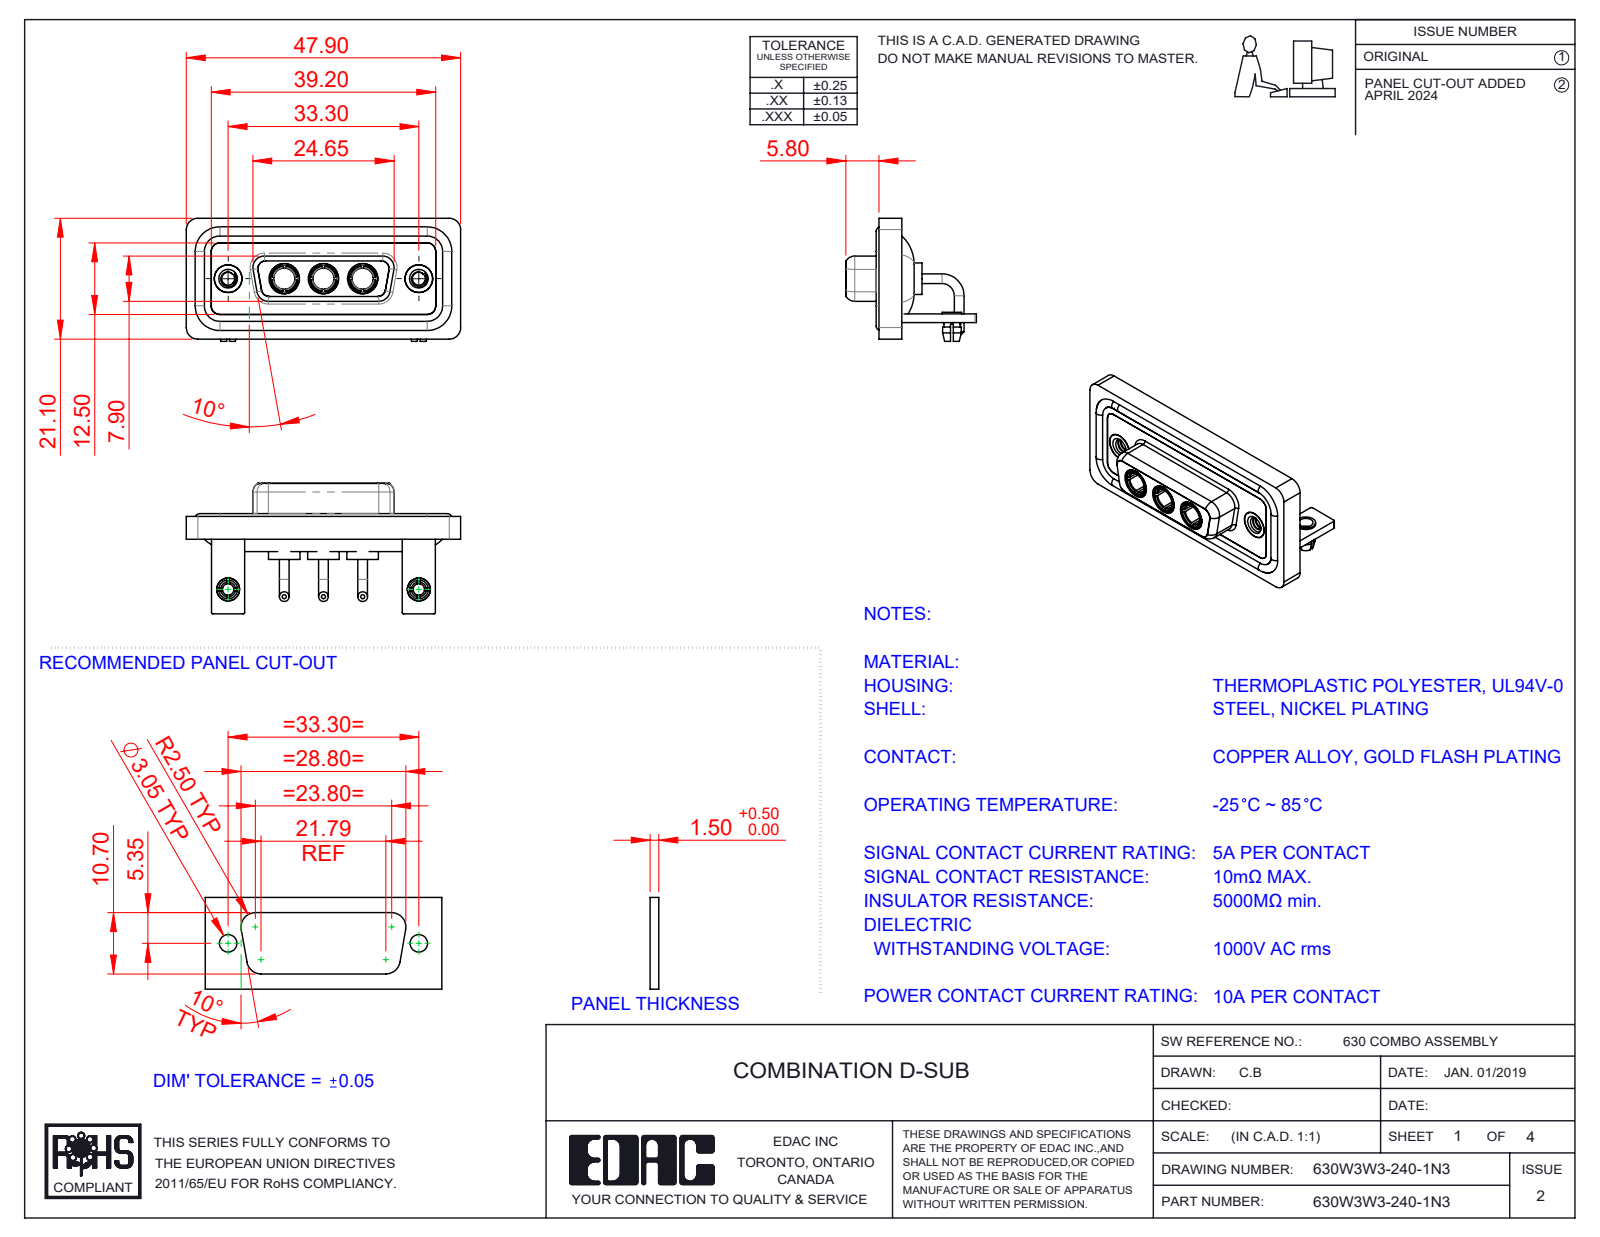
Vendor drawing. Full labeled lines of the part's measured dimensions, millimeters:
Part name (STEP PRODUCT): 630Combo Board Lock_50 Contacts; 630Combo Shell Rear_15 Contacts; 630W3W3-140-1N3; 630Combo Housing_3W3 (+5 more)
STEP written by: SolidWorks 2023 (CONFIG_CONTROL_DESIGN)
Units: millimetres
Bodies: 17 solids, 760 faces (260 planar, 319 cylindrical, 181 other)
Overall size (bounding box): 47.9 × 22.8 × 21.5
Volume: 6 409 mm³ · Surface area: 10 765 mm²
Round holes (diameter × count): ⌀4.85 ×5, ⌀3.7 ×3, ⌀5.3 ×3, ⌀2 ×2, ⌀2.26 ×2, ⌀2.5 ×2, ⌀3.2 ×2, ⌀4 ×2, ⌀4.05 ×2, ⌀5 ×2
Round bosses / shafts (diameter × count): ⌀1.7 ×6, ⌀1.6 ×4, ⌀5.5 ×3, ⌀5.2 ×3, ⌀4.96 ×3, ⌀4.75 ×3, ⌀3.75 ×3, ⌀4.95 ×2
Partial cylindrical surfaces — rounded edges, fillets, slot ends (radius × count): R2 ×21, R1.5 ×18, R0.25 ×16, R1.35 ×12, R1.6 ×8, R0.5 ×5, R0.6 ×4, R0.65 ×4
Main face-to-face distances: 0.4, 2.9, 1.5, 1.8, 3.7, 1.1, 4.1, 1.6, 2.5, 1.4
Hole centre spacings: 6.85, 9.8, 16.65, 23.5, 33.3, 13.7
